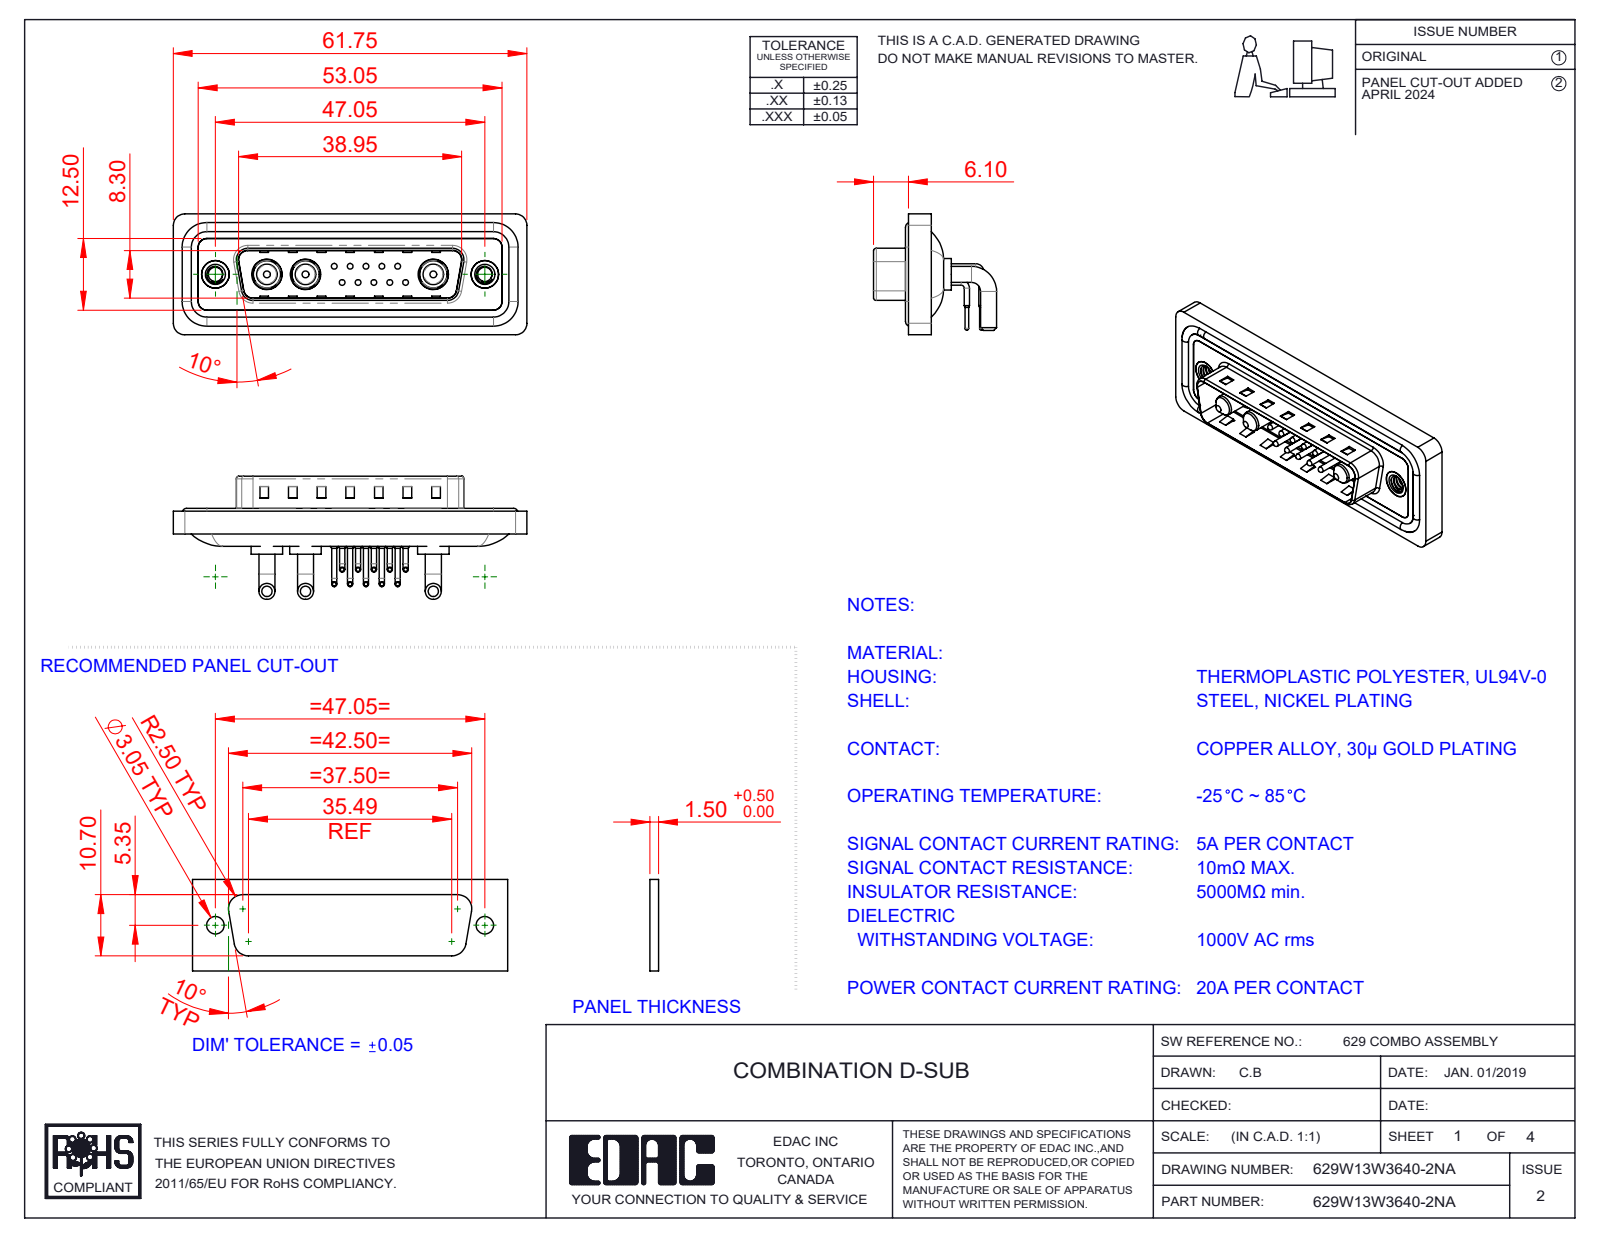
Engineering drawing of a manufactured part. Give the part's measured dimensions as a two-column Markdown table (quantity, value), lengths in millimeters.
| quantity | value |
| --- | --- |
| part name | Power Pin_20A RA; 629Combo Threaded Rivet_A; 629Combo Contact Row 2; 629Combo Shell Front_25 Contacts (+5 more) |
| STEP written by | SolidWorks 2023 (CONFIG_CONTROL_DESIGN) |
| units | millimeters |
| bodies | 23 solids, 1706 faces (879 planar, 609 cylindrical, 218 other) |
| overall size | 61.75 × 21.5 × 21.1 |
| volume | 7 613 mm³ |
| surface area | 12 500 mm² |
| round holes (diameter × count) | 0.75 × 10, 1.6 × 10, 2 × 10, 4.85 × 3, 5.3 × 3, 2.5 × 2, 4 × 2, 4.8 × 2, 5 × 2 |
| round bosses / shafts (diameter × count) | 0.9 × 20, 1.5 × 10, 1 × 10, 0.65 × 10, 2.8 × 6, 1.6 × 4, 5.5 × 3, 5.2 × 3 |
| partial cylindrical surfaces (radius × count) | 1.5 × 18, 2 × 18, 1.01 × 10, 0.5 × 8, 1.6 × 8, 0.25 × 4, 0.6 × 4, 0.65 × 4 |
| main face-to-face distances | 0.4, 2.9, 0.8, 4.1, 1.1, 2.1, 1.6, 4.5, 1.5, 6 |
| hole center spacings | 3.16, 2.77, 5.04, 5.54, 7.49, 5.03, 8.31, 10.11 |
